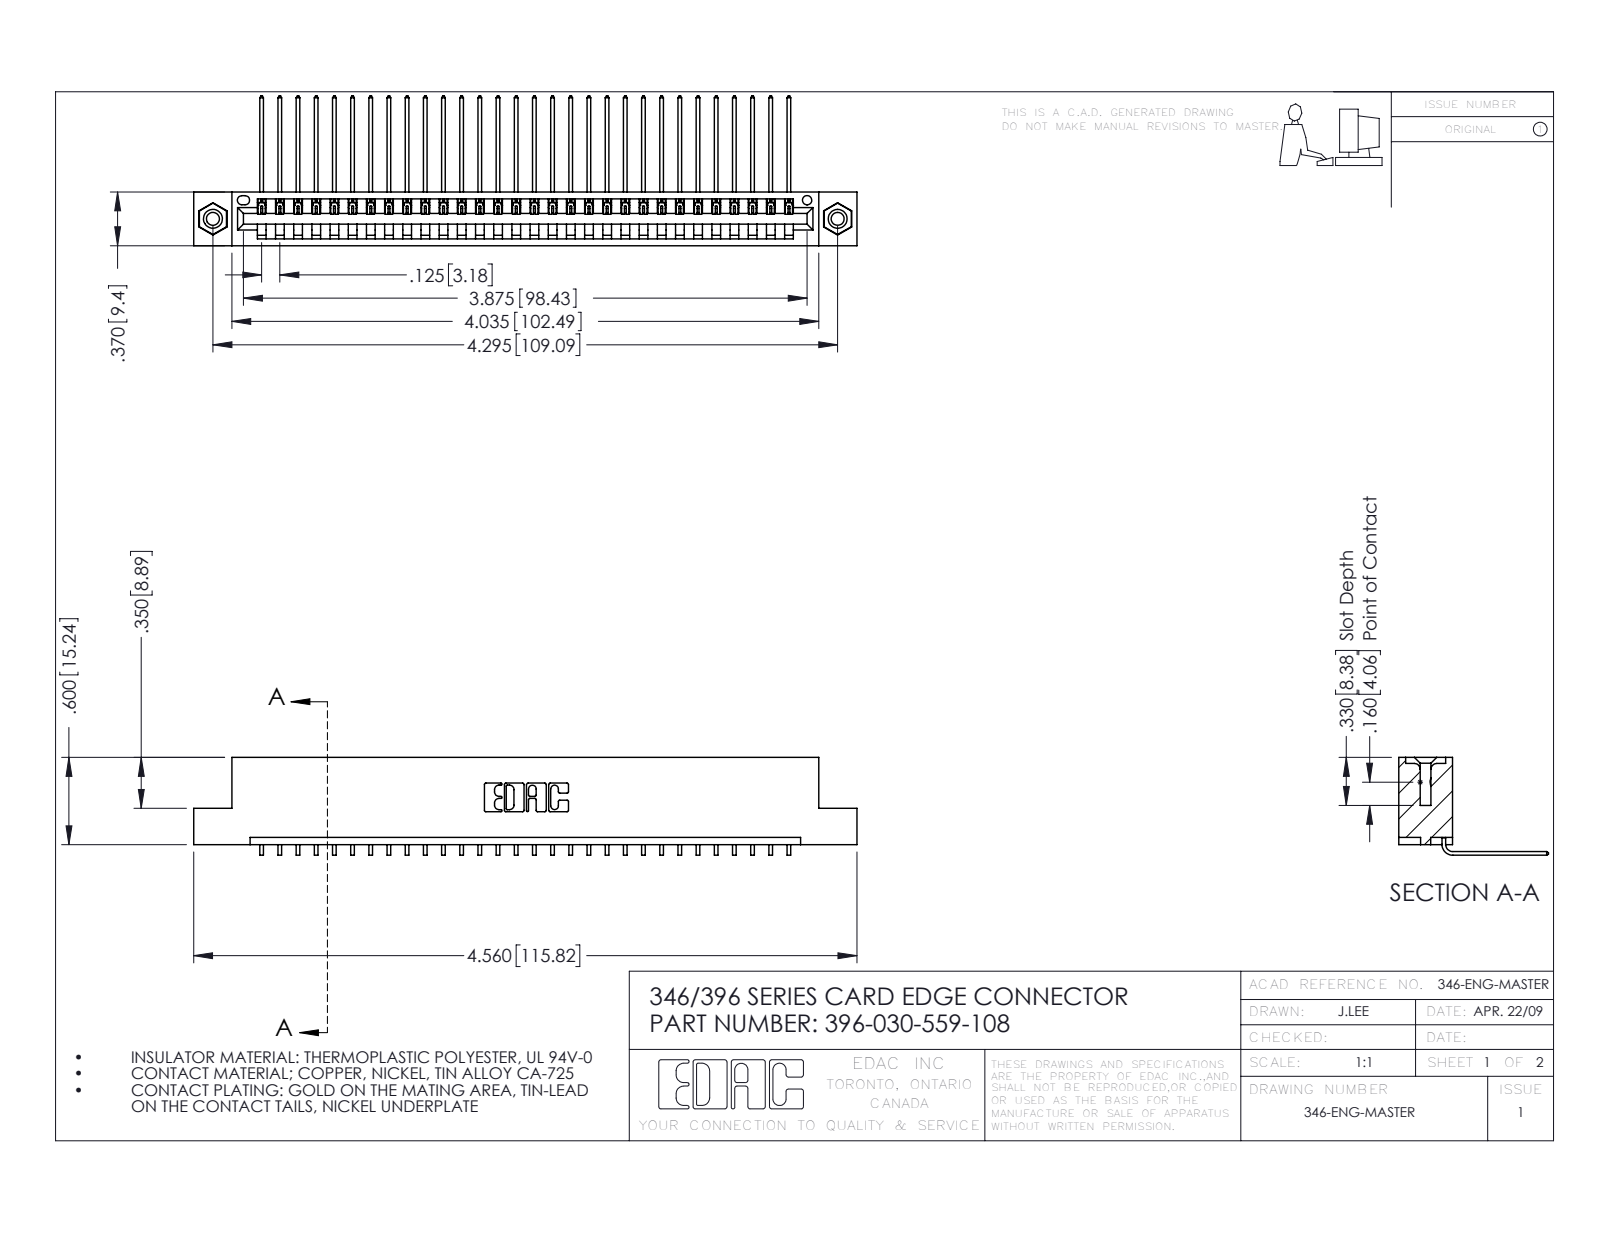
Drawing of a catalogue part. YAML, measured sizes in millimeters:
part_name: "345-292-001_558 559 Tail - 1; 345-250-001_345-250-003-102; 346 Part_Flush Mounting Lugs - 0.156 Dia-TI; 396-030-559-108"
step_written_by: "SolidWorks 2016 (CONFIG_CONTROL_DESIGN)"
units: millimeters
bodies: {solids: 33, faces: 1982, planar: 1368, cylindrical: 598, other: 16}
overall_size: [115.8, 26.2, 17.1]
volume: 11100
surface_area: 14360
round_holes:
  - {diameter: 2.3, count: 2}
  - {diameter: 3.2, count: 2}
  - {diameter: 4, count: 2}
  - {diameter: 1.6, count: 1}
round_bosses_or_shafts:
  - {diameter: 3.9, count: 2}
partial_cylinders:
  - {radius: 0.2, count: 60}
  - {radius: 0.3, count: 22}
  - {radius: 0.2, count: 6}
  - {radius: 0.8, count: 6}
  - {radius: 0.7, count: 3}
  - {radius: 0.8, count: 2}
  - {radius: 1, count: 2}
  - {radius: 0.4, count: 1}
face_to_face_distances: [1.2, 8.2, 9.4, 6.4, 1.8, 0.6, 7.6, 3.8, 5.6, 2.5]
hole_center_spacings: [6.2, 103.8, 109.1]
